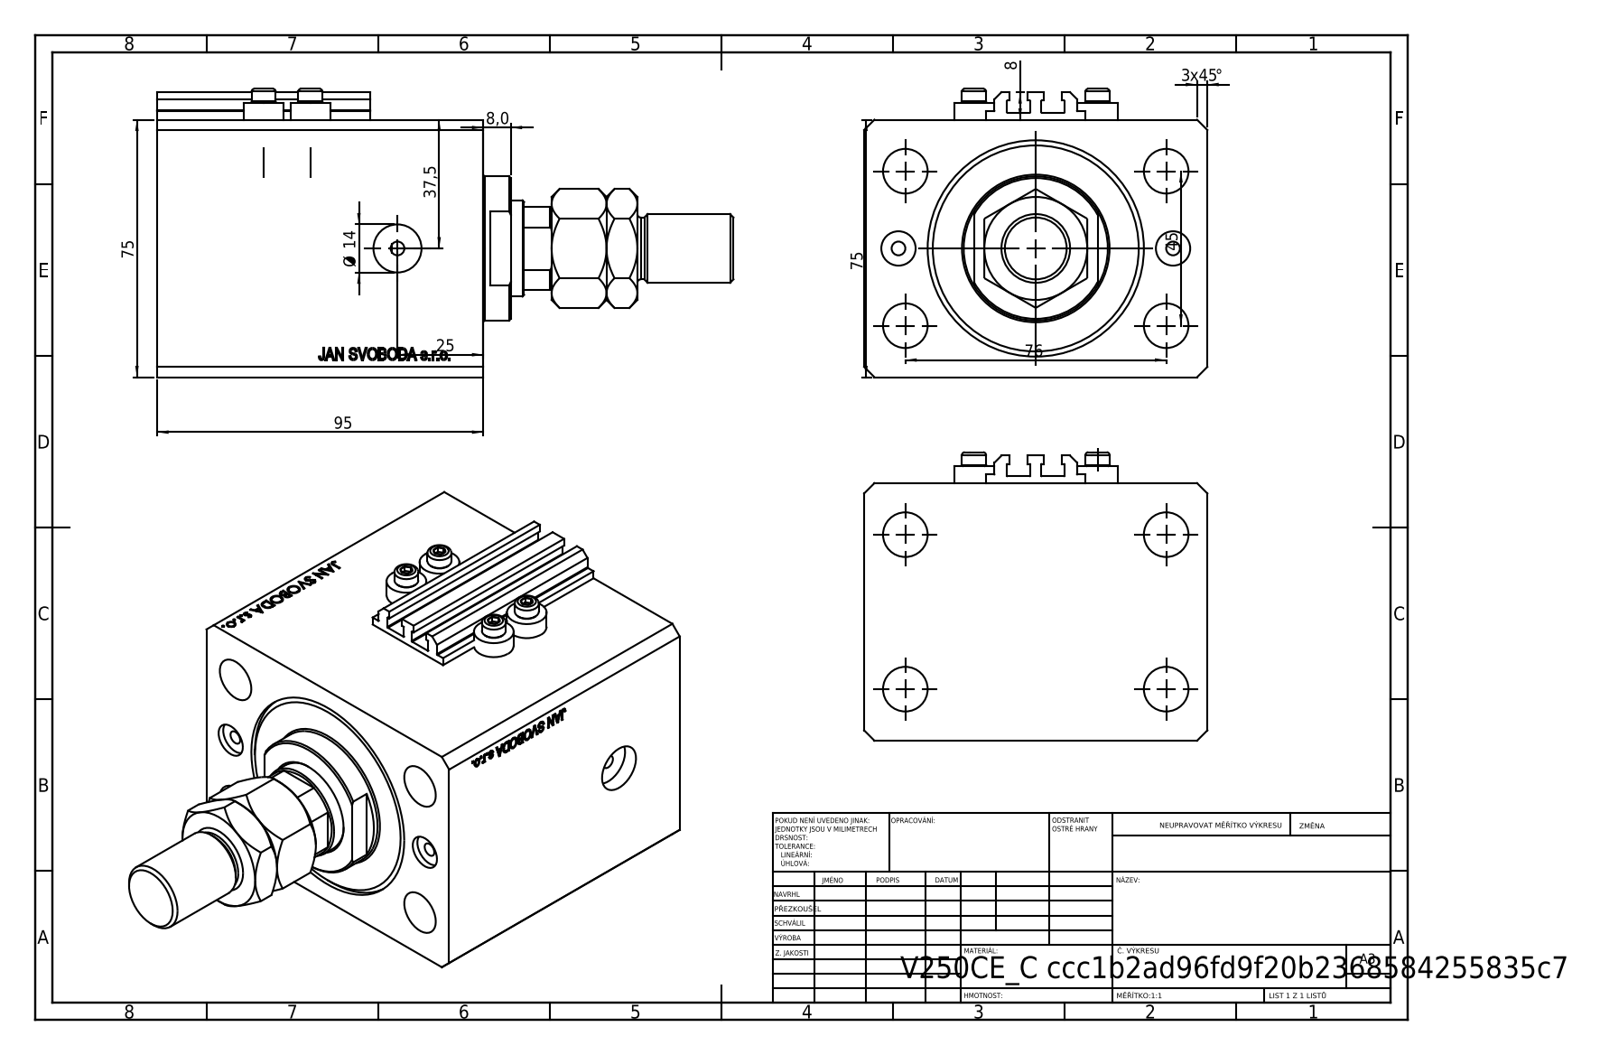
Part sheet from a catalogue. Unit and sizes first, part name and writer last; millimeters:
Units: millimetres
Overall size (bounding box): 167.9 × 100 × 84
Round holes (diameter × count): ⌀4 ×8, ⌀13 ×4, ⌀10 ×2, ⌀14 ×2, ⌀18.5 ×1, ⌀28 ×1, ⌀50 ×1, ⌀63 ×1
Round bosses / shafts (diameter × count): ⌀11.6 ×4, ⌀7 ×4, ⌀42 ×1, ⌀20 ×1, ⌀18 ×1
Partial cylindrical surfaces — rounded edges, fillets, slot ends (radius × count): R0.2 ×10, R13.5 ×1
Main face-to-face distances: 75, 100, 95, 11.9, 83.1, 68.4, 56.5, 26.6, 3, 48.4
Hole centre spacings: 22.59, 44.16, 81.18, 45, 13.6, 36, 38.48, 40
Volume: 675 923 mm³ · Surface area: 124 574 mm²
Bodies: 9 solids, 1083 faces (519 planar, 90 cylindrical, 474 other)
Part name (STEP PRODUCT): MTA; V250CE_C_VCP; V250CE_C_Body; V250CE_VC_C (+1 more)
STEP written by: SolidWorks 2019 (CONFIG_CONTROL_DESIGN)
